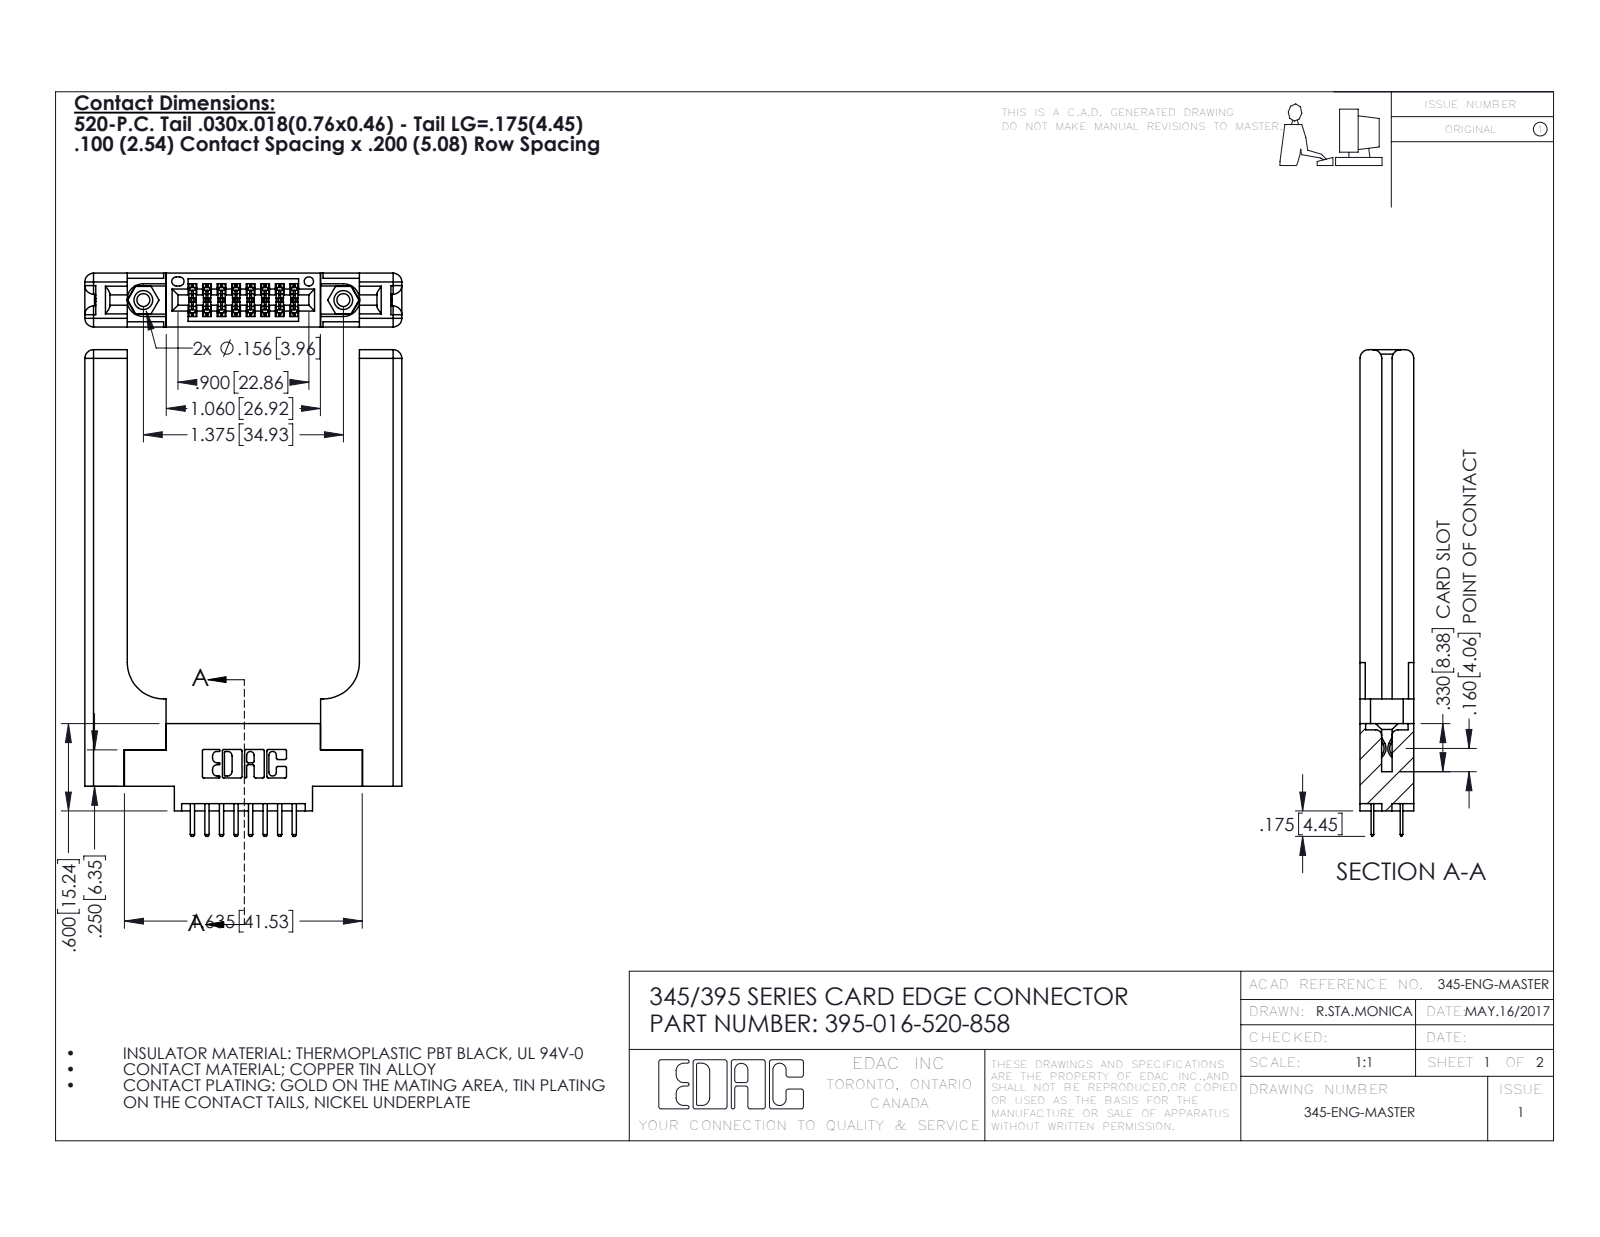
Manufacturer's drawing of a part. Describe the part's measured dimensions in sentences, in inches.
The part is named "345 Part_0.170 Offset - 0.156 Dia-TH; 395-016-520-858; 345-220-058_345-220-058; 345-250-001_345-250-001-102 (+1 more)". Its 3-D file was written by "SolidWorks 2016 (CONFIG_CONTROL_DESIGN)". It is 21 solids with 1250 faces: 792 planar, 398 cylindrical and 60 other. Overall it measures 3.345 by 2.179 by 0.37 inches. Its volume is 0.819 cubic inches and its surface area 18.34 square inches. Round holes: 2 of diameter 0.089, 2 of diameter 0.125, 2 of diameter 0.156, 1 of diameter 0.064. Round bosses or shafts: 2 of diameter 0.155. Partial cylindrical surfaces (rounded edges, fillets, slot ends): 24 of radius 0.006, 22 of radius 0.01, 20 of radius 0.01, 16 of radius 0.06, 6 of radius 0.007, 6 of radius 0.031, 3 of radius 0.026, 2 of radius 0.014. The main face-to-face distances are 0.37, 0.15, 0.22, 0.072, 0.298, 0.077, 0.148, 1.596, 0.071, 0.12. The hole center spacings are 0.27, 1.144, 1.375.
